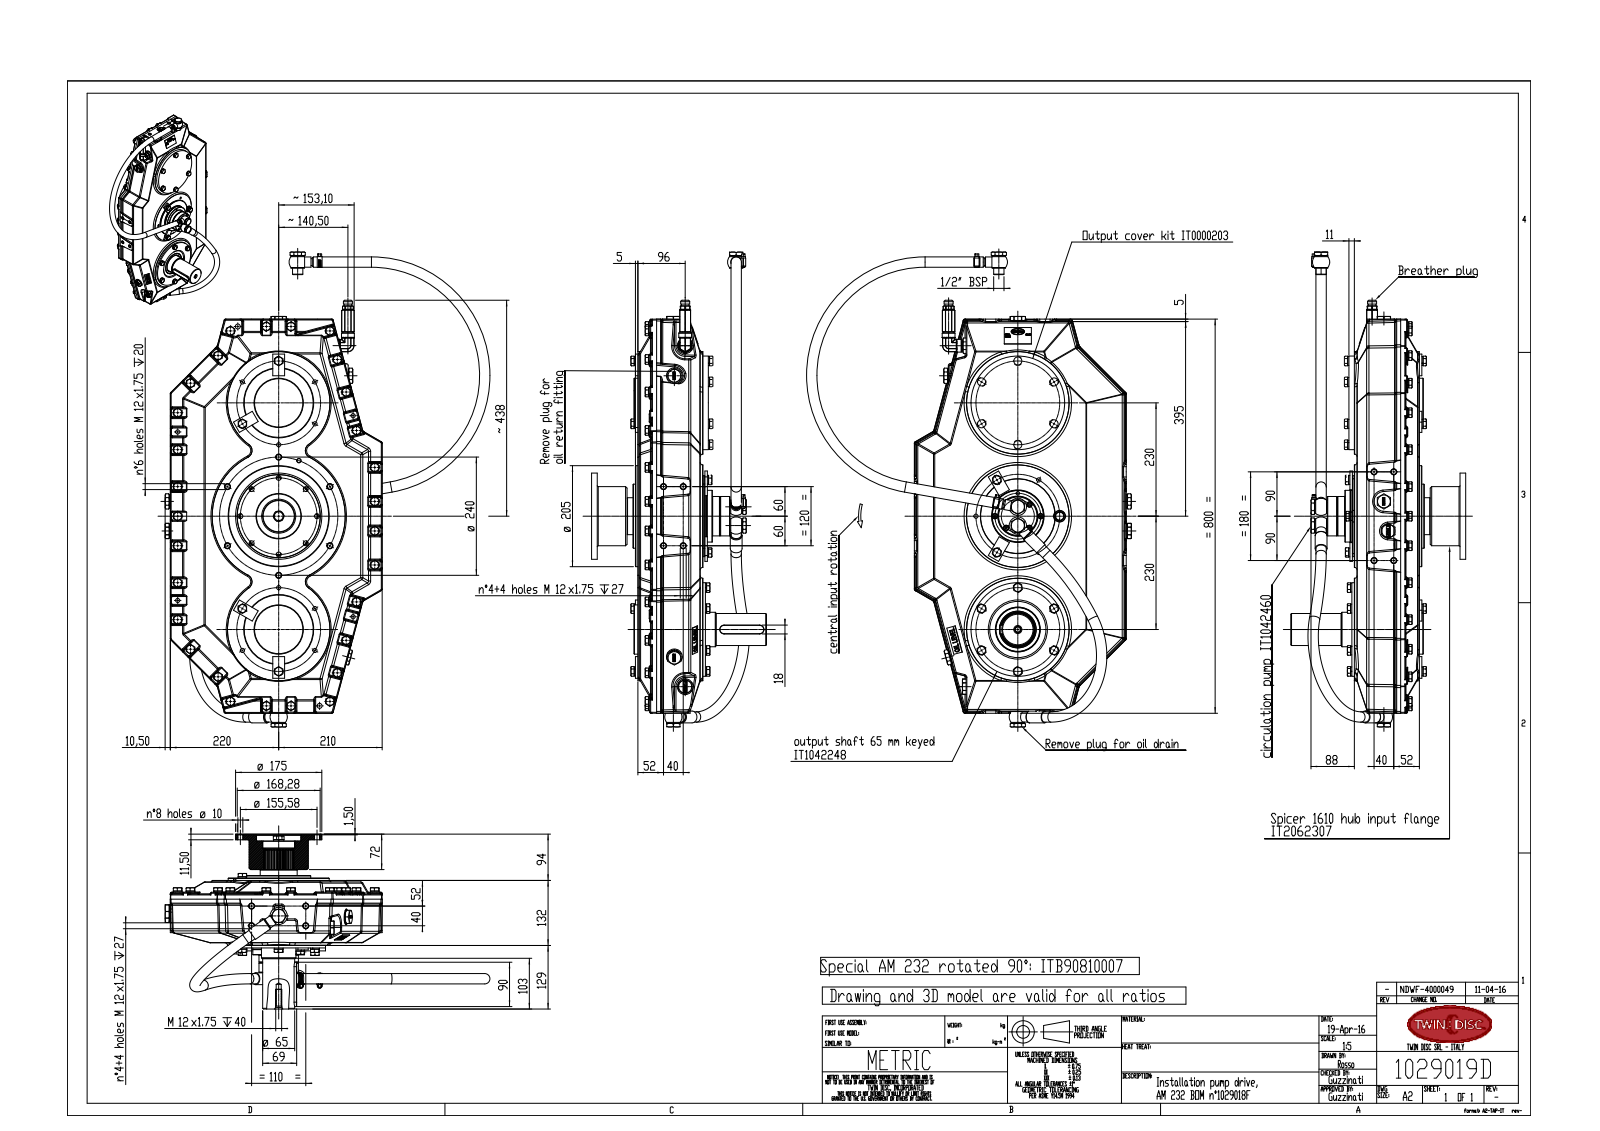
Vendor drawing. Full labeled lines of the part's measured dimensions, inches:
Part name (STEP PRODUCT): IT0000394_rev00-installation; 1029019D; ITB90810000_rev00-installation; IT2062307_rev02-installation (+7 more)
STEP written by: SolidWorks 2007 (AUTOMOTIVE_DESIGN)
Units: inches
Bodies: 57 solids, 8477 faces (3127 planar, 2795 cylindrical, 2555 other)
Overall size (bounding box): 37.962 × 25.954 × 13.976
Volume: 303.5 in³ · Surface area: 3 717 in²
Round holes (diameter × count): ⌀0.402 ×64, ⌀0.413 ×35, ⌀0.335 ×30, ⌀0.394 ×20, ⌀0.472 ×20, ⌀0.433 ×17, ⌀0.827 ×11, ⌀0.315 ×10, ⌀0.512 ×10, ⌀0.276 ×7, ⌀0.197 ×6, ⌀1.26 ×5
Round bosses / shafts (diameter × count): ⌀0.394 ×50, ⌀0.713 ×44, ⌀0.638 ×44, ⌀1.063 ×7, ⌀0.236 ×6, ⌀1.024 ×5, ⌀0.709 ×5, ⌀1.053 ×4
Partial cylindrical surfaces — rounded edges, fillets, slot ends (radius × count): R0.079 ×284, R0.197 ×112, R0.098 ×84, R0.118 ×80, R0.018 ×58, R0.02 ×24, R0.059 ×16, R0.039 ×6
Main face-to-face distances: 0.118, 4.98, 5.197, 0.65, 0.217, 4.862, 5.512, 0.157, 0.315, 5.079
Hole centre spacings: 3.346, 5.796, 16.691, 19.994, 18.11, 1.295, 1.575, 2.917
